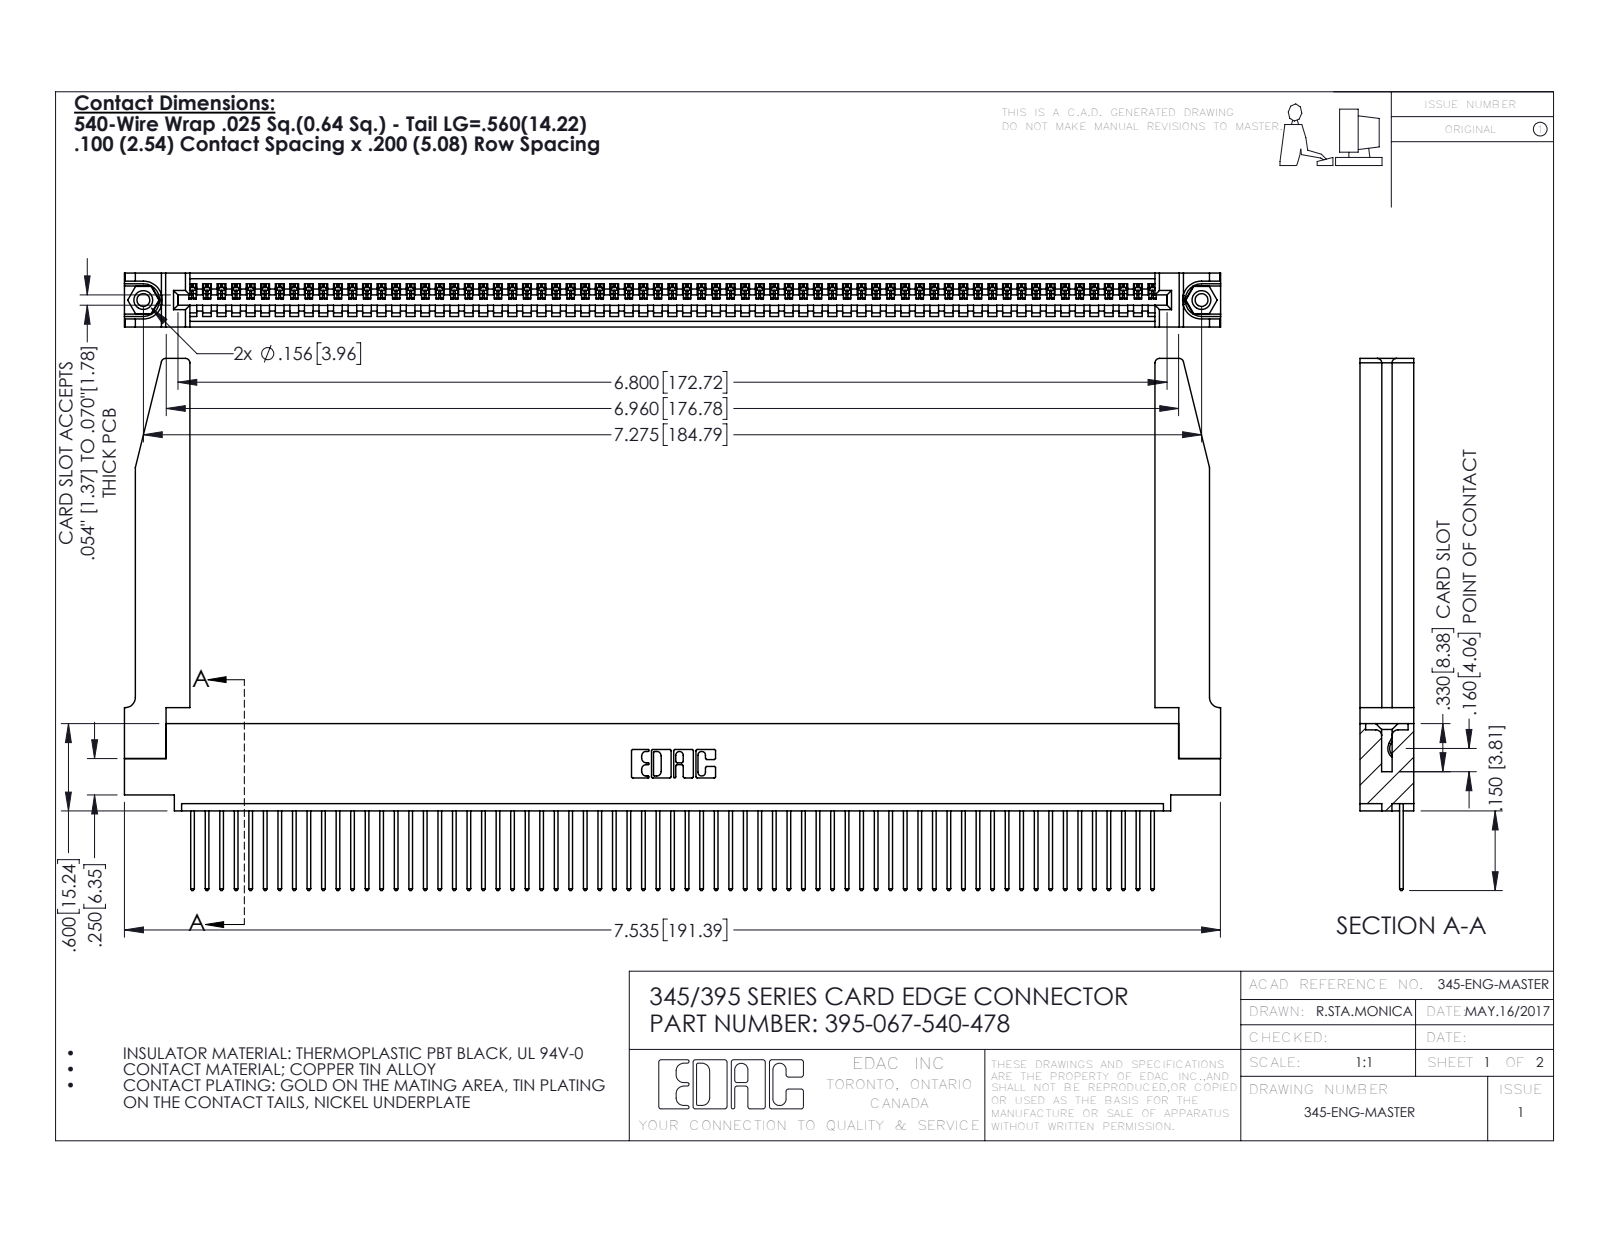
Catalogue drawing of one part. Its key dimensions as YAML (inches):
part_name: "395-067-540-478; 345-292-001_345-293-140; 345-220-078_345-220-078; 345 Part_0.110 Offset - 0.156 Dia-TH (+1 more)"
step_written_by: "SolidWorks 2016 (CONFIG_CONTROL_DESIGN)"
units: inches
bodies: {solids: 72, faces: 4250, planar: 2906, cylindrical: 1292, other: 52}
overall_size: [7.536, 3.657, 0.37]
volume: 1.597
surface_area: 50.18
round_holes:
  - {diameter: 0.089, count: 2}
  - {diameter: 0.125, count: 2}
  - {diameter: 0.156, count: 2}
  - {diameter: 0.064, count: 1}
round_bosses_or_shafts:
  - {diameter: 0.155, count: 2}
partial_cylinders:
  - {radius: 0.006, count: 134}
  - {radius: 0.01, count: 134}
  - {radius: 0.01, count: 22}
  - {radius: 0.03, count: 8}
  - {radius: 0.007, count: 6}
  - {radius: 0.031, count: 6}
  - {radius: 0.026, count: 3}
  - {radius: 0.031, count: 2}
face_to_face_distances: [0.072, 0.298, 0.37, 0.098, 0.272, 0.025, 0.2, 0.225, 0.149, 0.148]
hole_center_spacings: [0.27, 7.039, 7.275]
